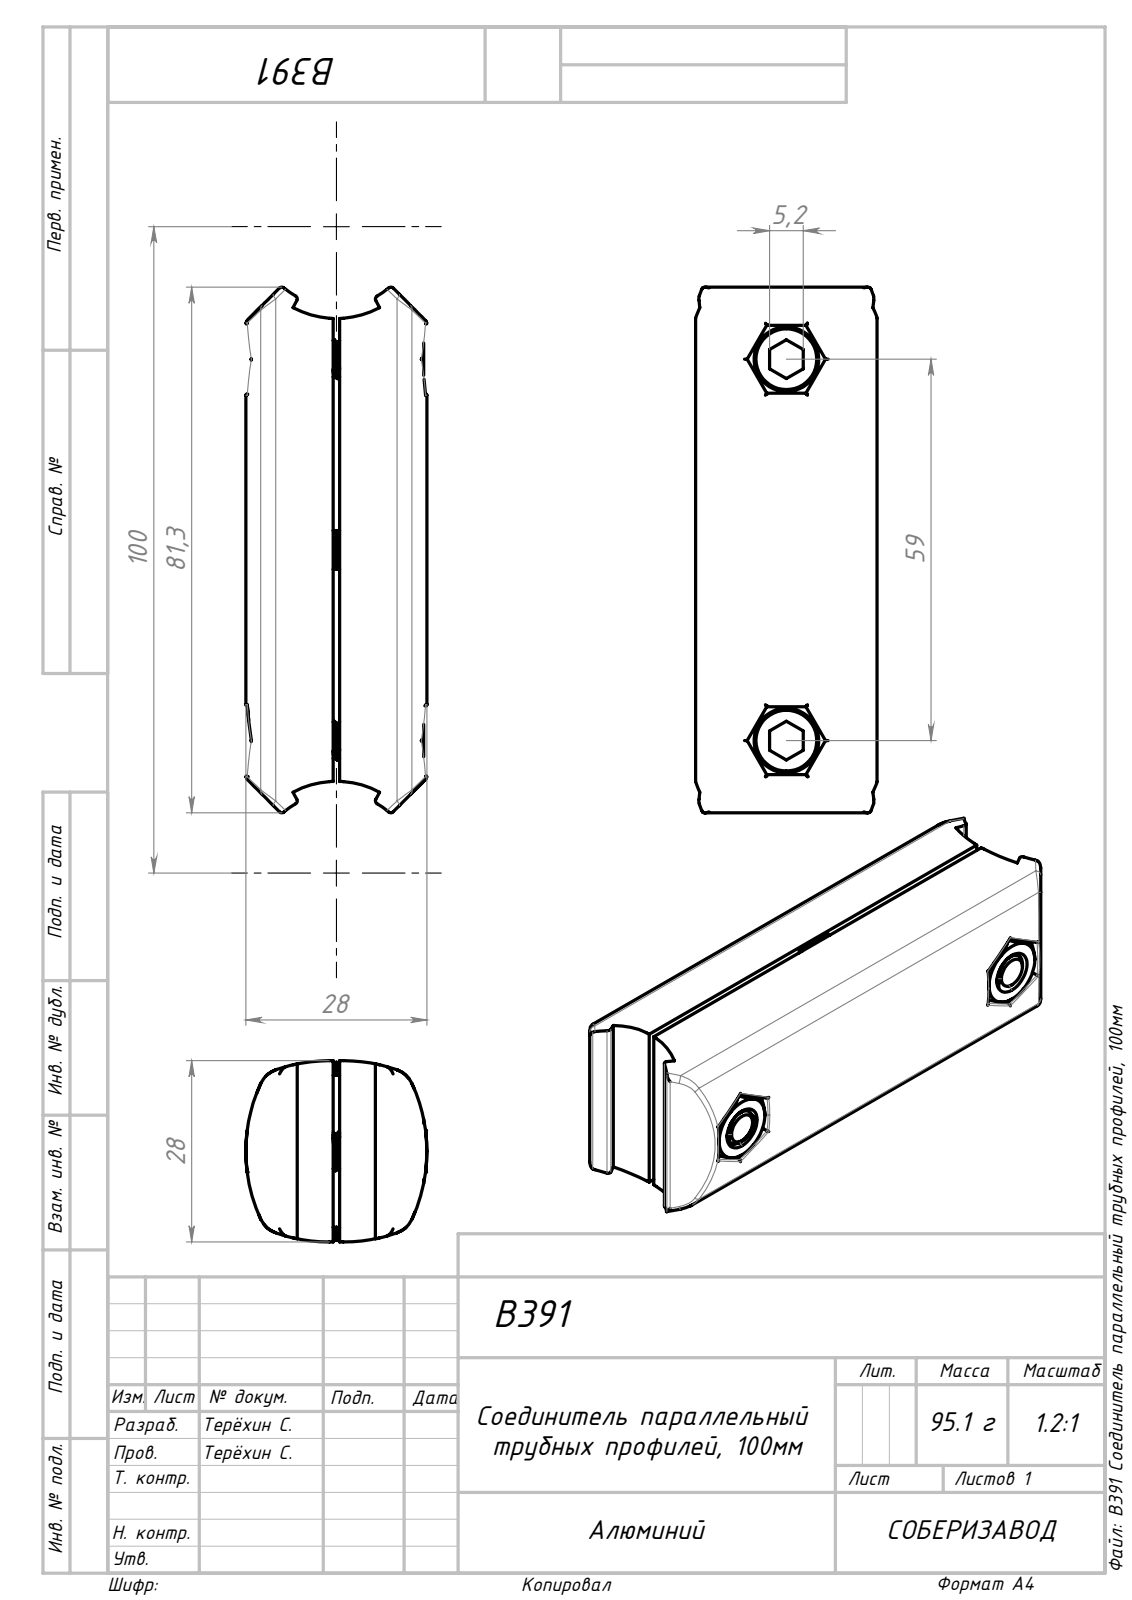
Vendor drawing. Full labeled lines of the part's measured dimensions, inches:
Part name (STEP PRODUCT): B391 Соединитель параллельный трубных профилей, 100мм
STEP written by: SolidWorks 2022 (AUTOMOTIVE_DESIGN)
Units: inches
Bodies: 6 solids, 576 faces (158 planar, 192 cylindrical, 226 other)
Overall size (bounding box): 3.202 × 1.104 × 1.102
Volume: 1.826 in³ · Surface area: 33.7 in²
Round holes (diameter × count): ⌀0.205 ×2, ⌀0.256 ×2
Round bosses / shafts (diameter × count): ⌀0.394 ×2, ⌀0.236 ×2
Partial cylindrical surfaces — rounded edges, fillets, slot ends (radius × count): R0.039 ×32, R0.02 ×8, R0.886 ×6, R0.984 ×6, R0.059 ×4, R0.157 ×4, R0.49 ×2, R0.559 ×2
Main face-to-face distances: 0.098, 0.039, 0.276, 0.236, 0.405, 1.161, 0.394, 0.512, 0.083, 0.674
Hole centre spacings: 2.323
